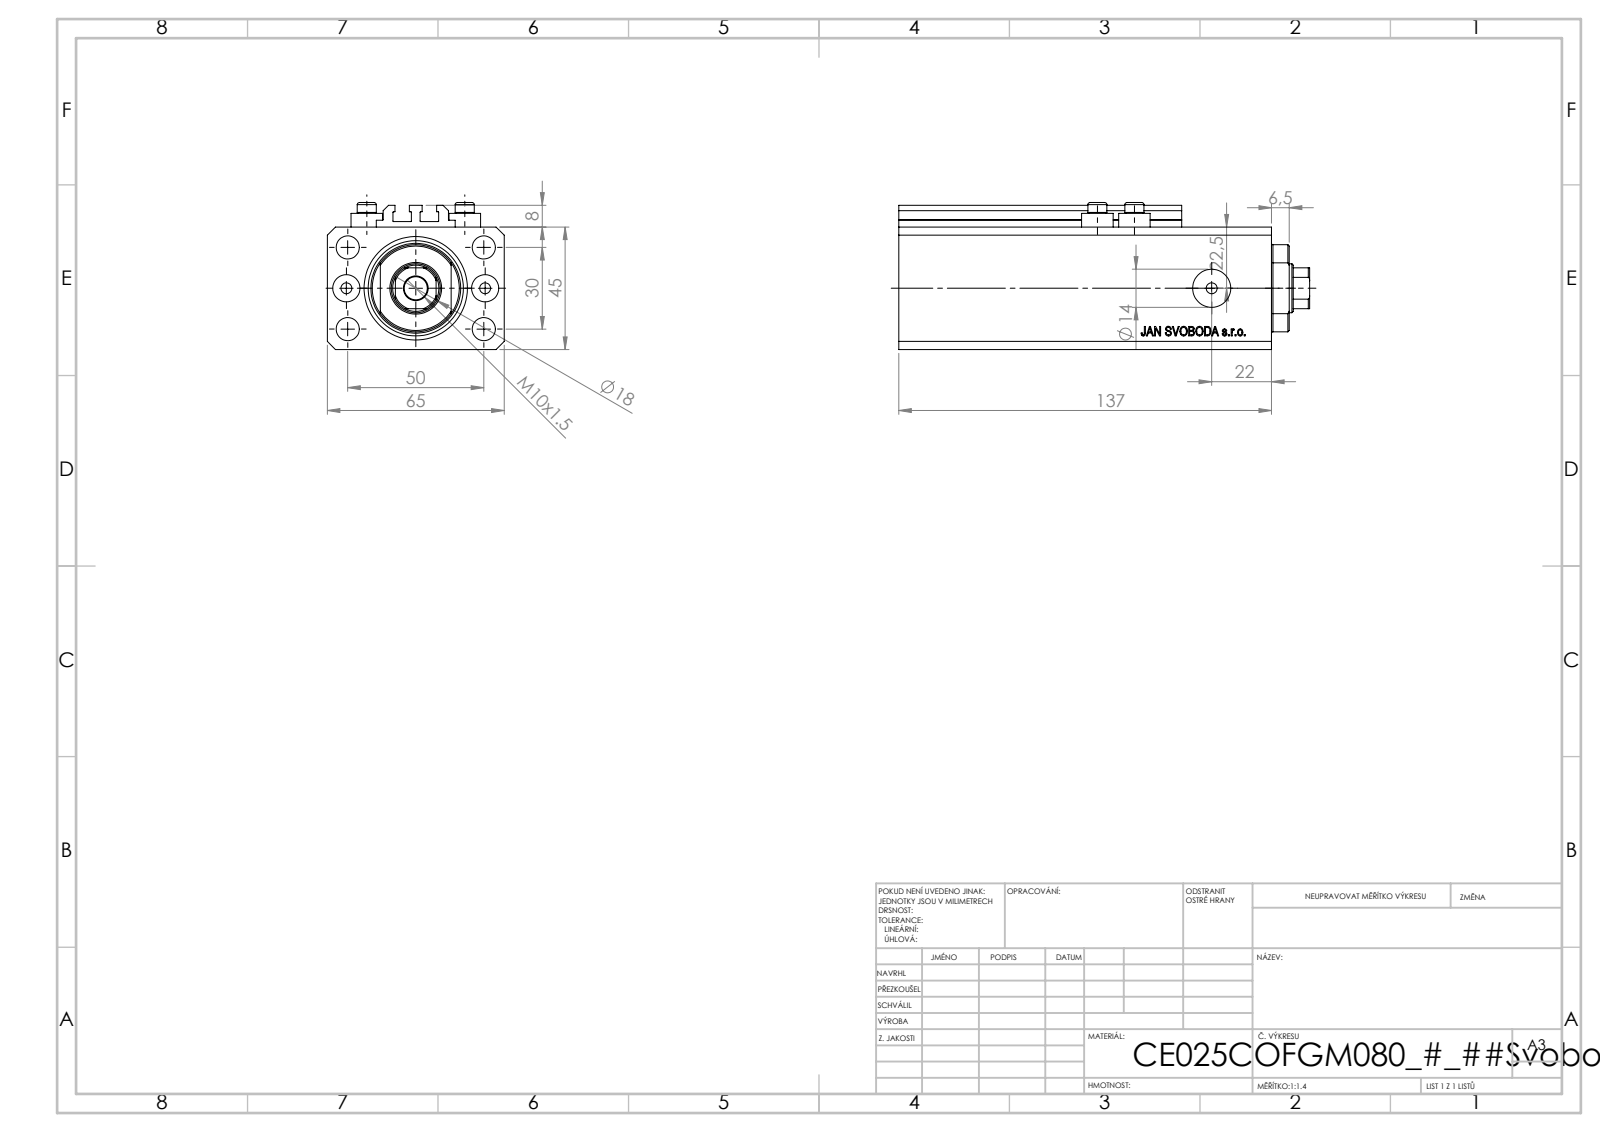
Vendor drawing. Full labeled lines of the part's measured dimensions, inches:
Part name (STEP PRODUCT): V250CE_C_VCP; V250CE_C_Body; V250CE_VC_C; ALLEN BOLT V250CE
STEP written by: SolidWorks 2019 (CONFIG_CONTROL_DESIGN)
Units: inches
Bodies: 8 solids, 1034 faces (504 planar, 86 cylindrical, 444 other)
Overall size (bounding box): 5.945 × 2.559 × 2.126
Volume: 22.34 in³ · Surface area: 140.4 in²
Round holes (diameter × count): ⌀0.157 ×8, ⌀0.335 ×5, ⌀0.394 ×2, ⌀0.551 ×2, ⌀0.709 ×1, ⌀0.984 ×1, ⌀1.496 ×1
Round bosses / shafts (diameter × count): ⌀0.457 ×4, ⌀0.276 ×4
Partial cylindrical surfaces — rounded edges, fillets, slot ends (radius × count): R0.008 ×10, R0.335 ×1, R0.63 ×1
Main face-to-face distances: 1.772, 2.559, 1.85, 0.551, 4.843, 5.394, 0.098, 0.079, 0.394, 0.807
Hole centre spacings: 0.591, 1.148, 2.074, 0.535, 1.004, 1.181, 1.417, 1.515
